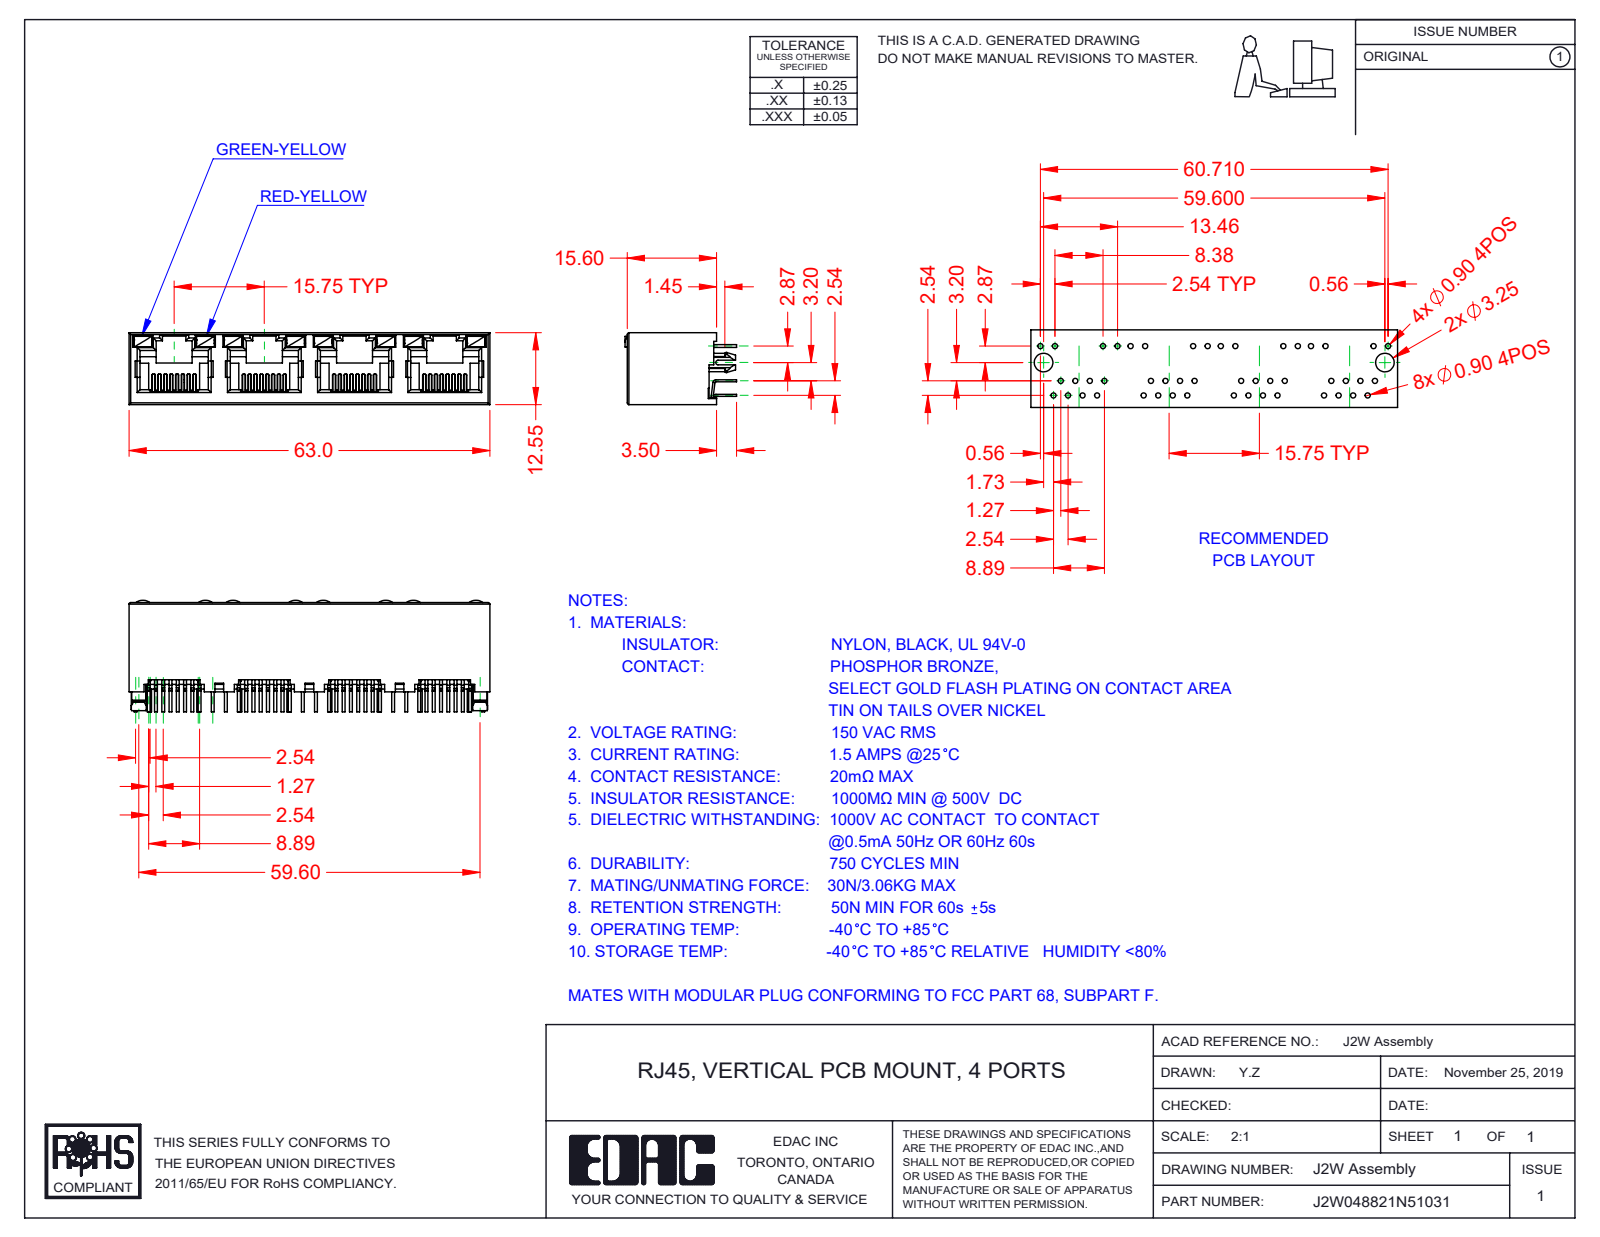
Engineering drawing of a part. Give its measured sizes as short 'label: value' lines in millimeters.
name: 2W Contacts; 2W LED RH_8-Red-Yellow; 2W LED LH_5-Green-Yellow; 2W Insulator (+2 more)
written by: SolidWorks 2016 (CONFIG_CONTROL_DESIGN)
unit: mm
bodies: 45 solids, 3143 faces (2600 planar, 485 cylindrical, 58 other)
size: 63 × 19.5 × 12.55
volume: 5 335 mm³; area: 13 144 mm²
rounds: 64× R0.15, 29× R0.2, 28× R0.5, 14× R0.3, 8× R0.45, 8× R2, 2× R0.25, 2× R1.5
face distances: 12.55, 11.9, 0.65, 15.75, 0.36, 1.5, 0.78, 0.6, 11.3, 31.5
